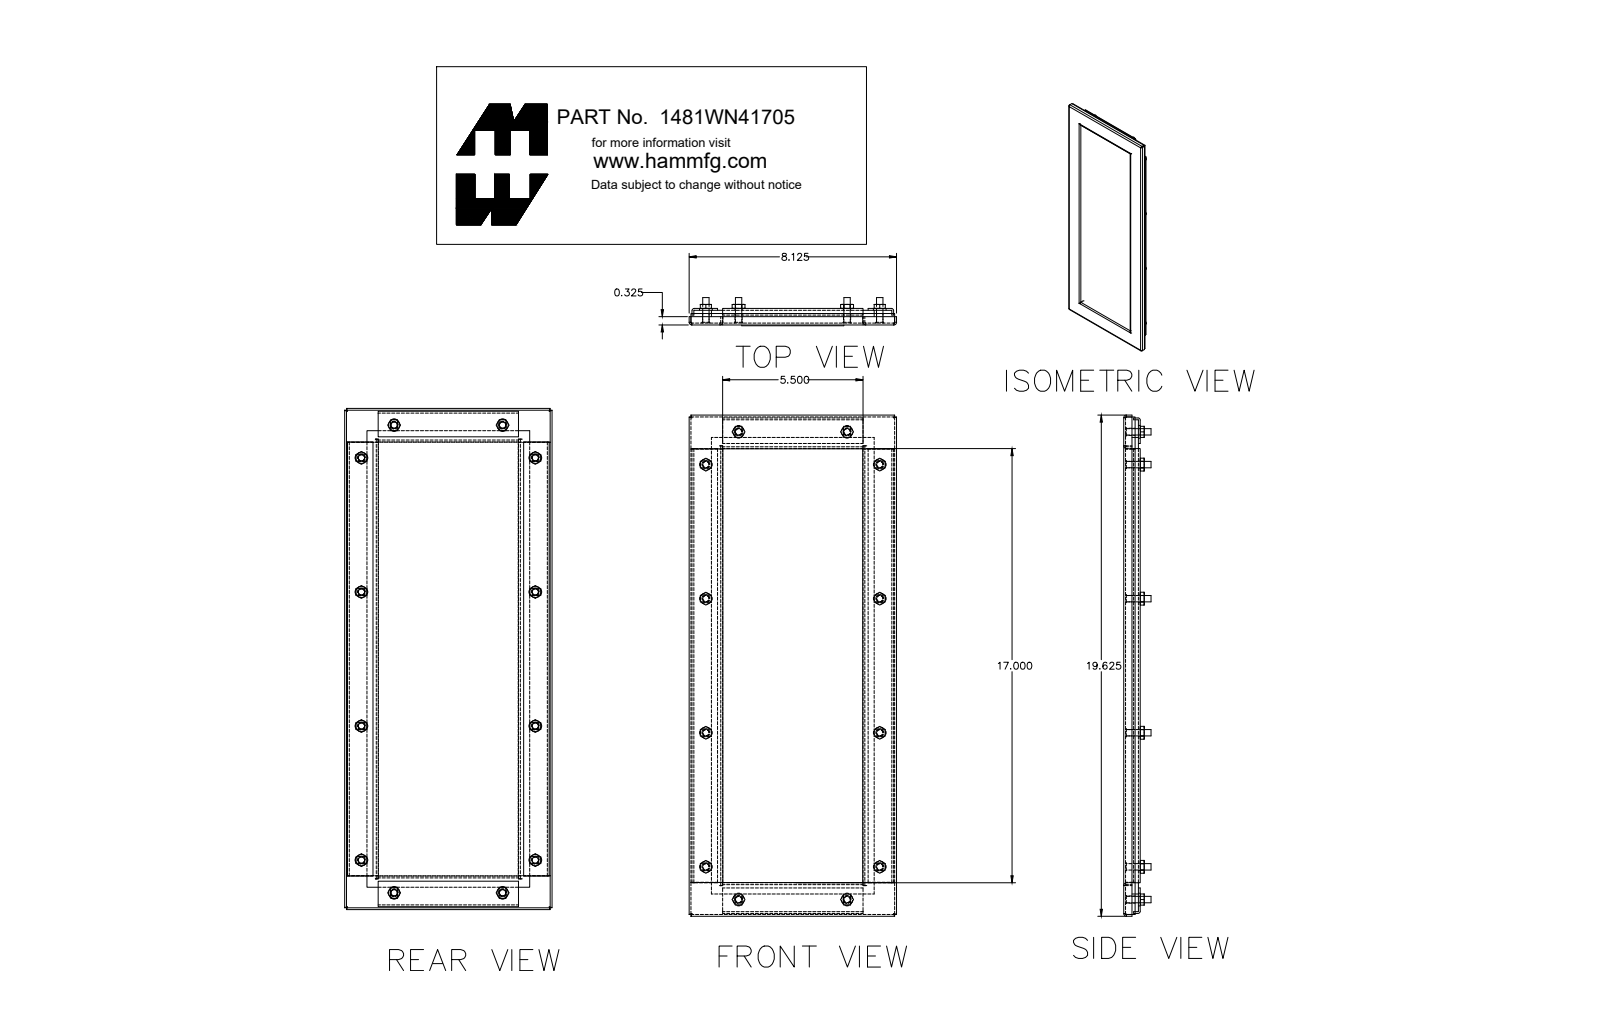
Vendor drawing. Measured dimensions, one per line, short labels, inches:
name: 1481WN41705_Default
written by: SolidWorks 2019 (CONFIG_CONTROL_DESIGN)
unit: in
bodies: 31 solids, 530 faces (246 planar, 120 cylindrical, 164 other)
size: 20.025 × 8.525 × 1.072
volume: 45.53 in³; area: 732.2 in²
holes: 12× ⌀0.25, 12× ⌀0.328
bosses: 12× ⌀0.313, 12× ⌀0.25
rounds: 8× R0.036, 8× R0.108, 4× R0.016, 4× R0.088
face distances: 0.072, 0.575, 0.503, 0.25, 0.325, 0.253, 0.575, 0.647, 0.322, 0.072
hole spacings: 6.813, 5.25, 8.601, 10.5, 18.313, 8.6, 8.601, 12.517
